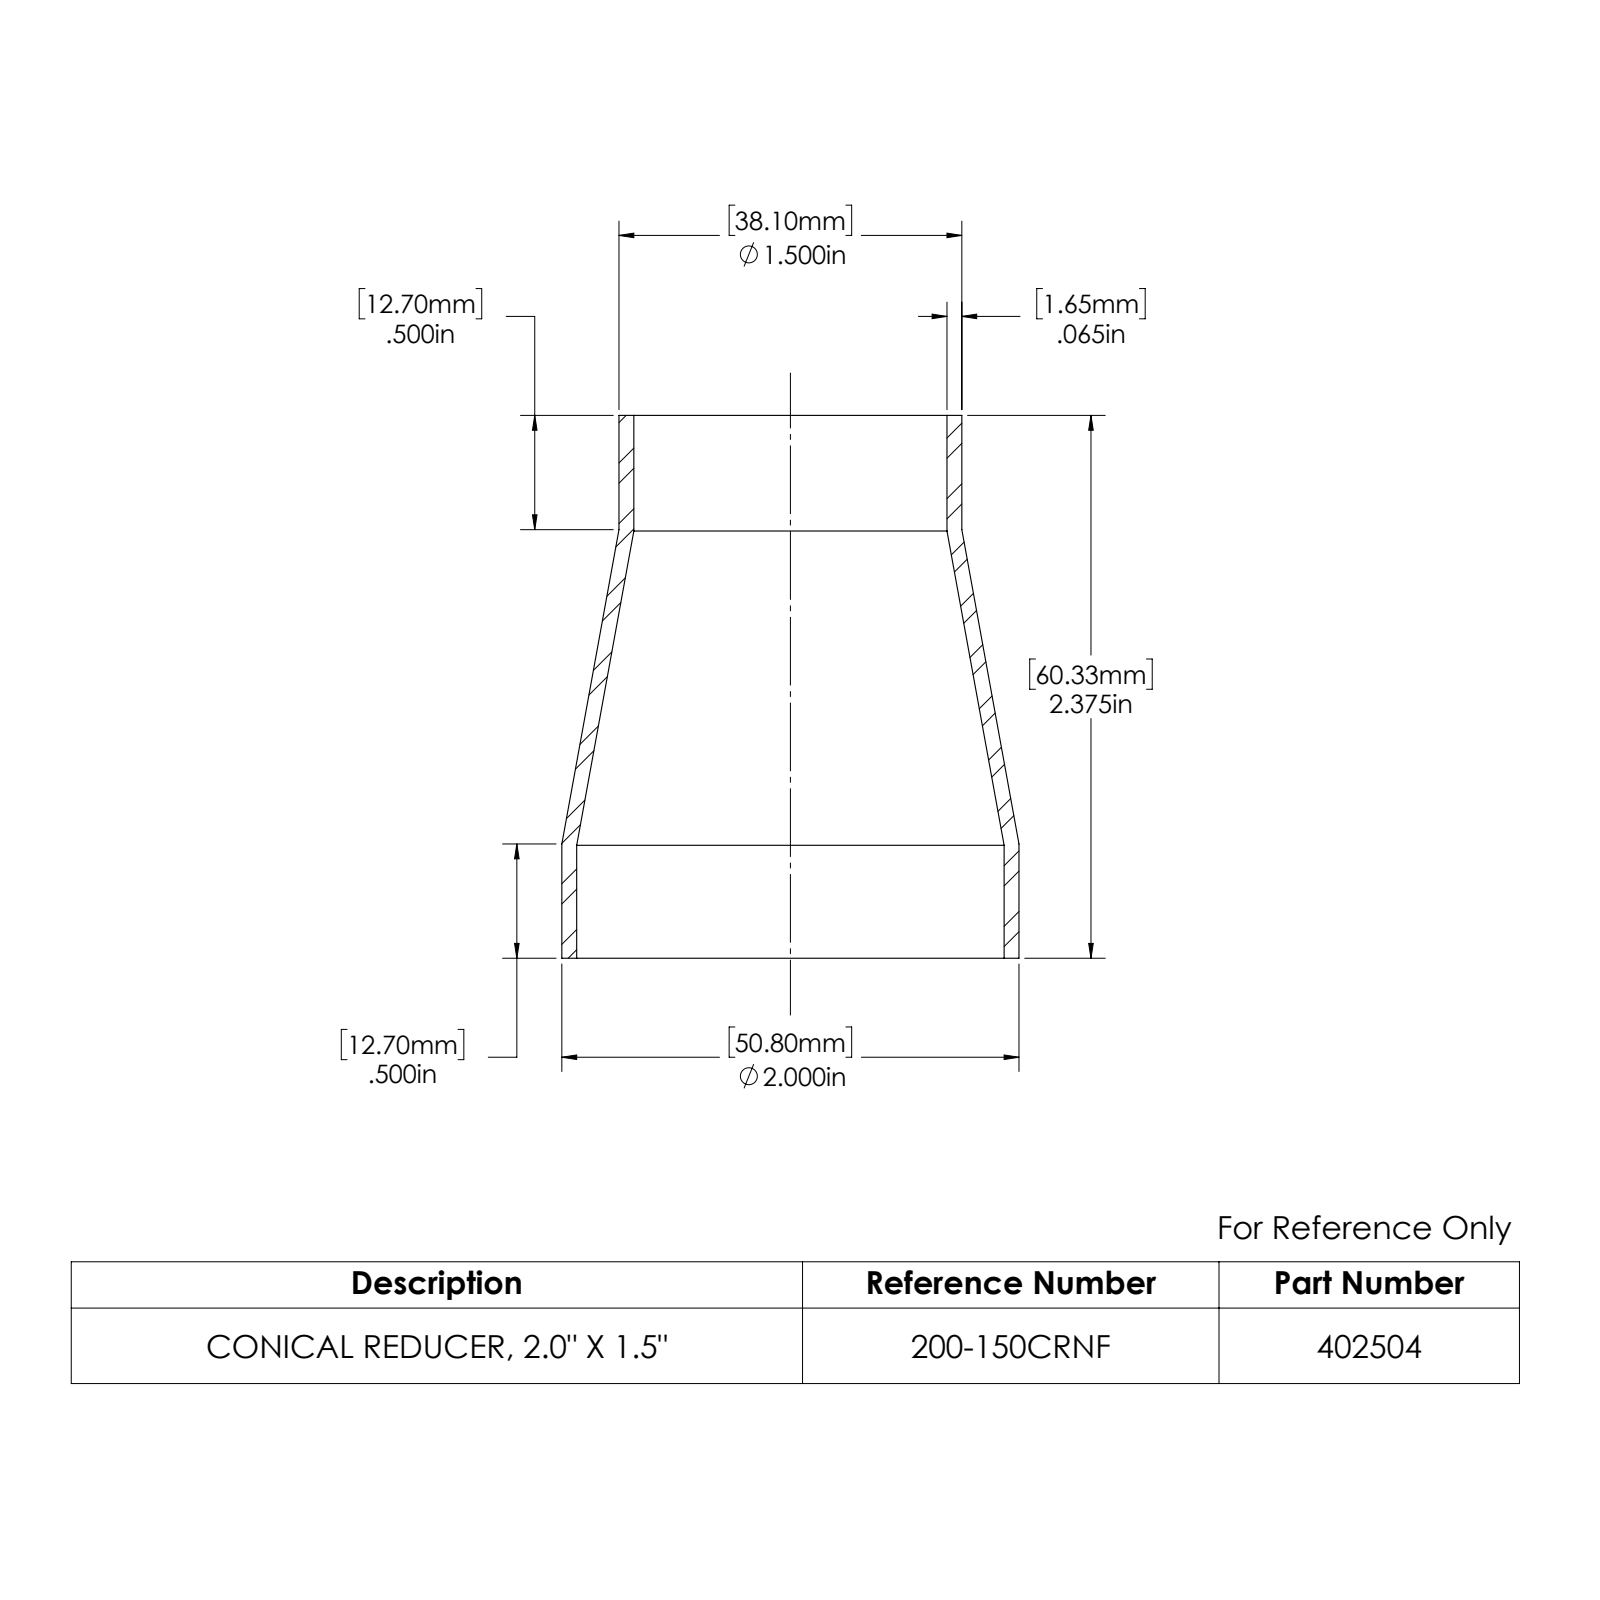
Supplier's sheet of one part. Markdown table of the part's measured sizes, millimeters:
| quantity | value |
| --- | --- |
| part name | 402504 |
| STEP written by | SolidWorks 2022 (AUTOMOTIVE_DESIGN) |
| units | millimeters |
| bodies | 1 solid, 14 faces (2 planar, 8 cylindrical, 4 other) |
| overall size | 60.3 × 50.8 × 50.8 |
| volume | 13 500 mm³ |
| surface area | 16 810 mm² |
| round holes (diameter × count) | 34.8 × 1, 47.5 × 1 |
| round bosses / shafts (diameter × count) | 50.8 × 1, 38.1 × 1 |
| main face-to-face distances | 60.3 |
